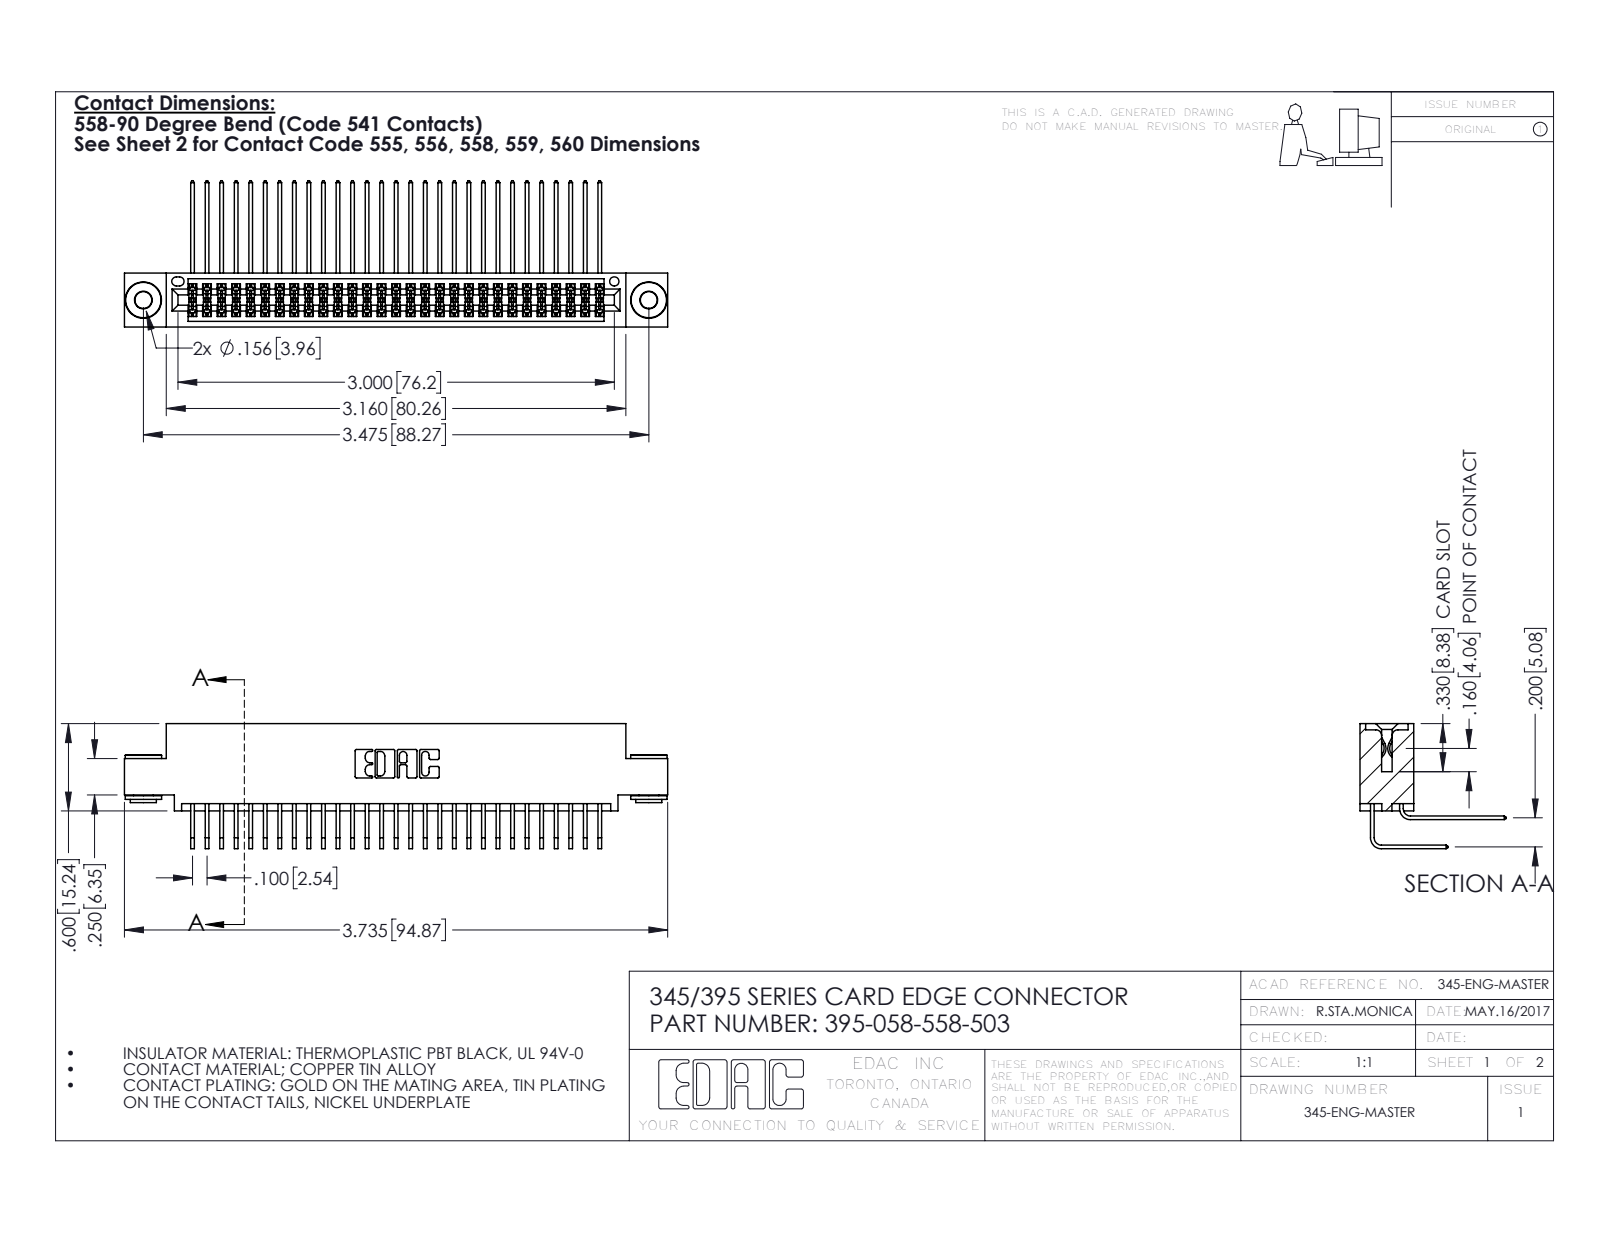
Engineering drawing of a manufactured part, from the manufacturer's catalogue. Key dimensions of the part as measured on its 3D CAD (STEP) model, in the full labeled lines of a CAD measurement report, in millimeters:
Part name (STEP PRODUCT): 345-292-001_558 Tail - 2; 345-292-001_558 559 Tail - 1; 345-250-002_345-250-002-102; 395-058-558-503 (+1 more)
STEP written by: SolidWorks 2016 (CONFIG_CONTROL_DESIGN)
Units: millimetres
Bodies: 61 solids, 3184 faces (2124 planar, 1052 cylindrical, 8 other)
Overall size (bounding box): 94.9 × 25.5 × 21.8
Volume: 9 370 mm³ · Surface area: 15 480 mm²
Round holes (diameter × count): ⌀2.9 ×2, ⌀4 ×2, ⌀1.6 ×1
Round bosses / shafts (diameter × count): ⌀6.4 ×2, ⌀4.6 ×2, ⌀3.5 ×2
Partial cylindrical surfaces — rounded edges, fillets, slot ends (radius × count): R0.2 ×88, R0.3 ×22, R0.2 ×6, R0.8 ×6, R0.7 ×3, R0.4 ×2, R0.5 ×2, R0.6 ×2
Main face-to-face distances: 1.8, 7.6, 5.1, 9.4, 0.6, 2.5, 6.9, 5.7, 0.6, 4.4
Hole centre spacings: 6.9, 82.3, 88.3
